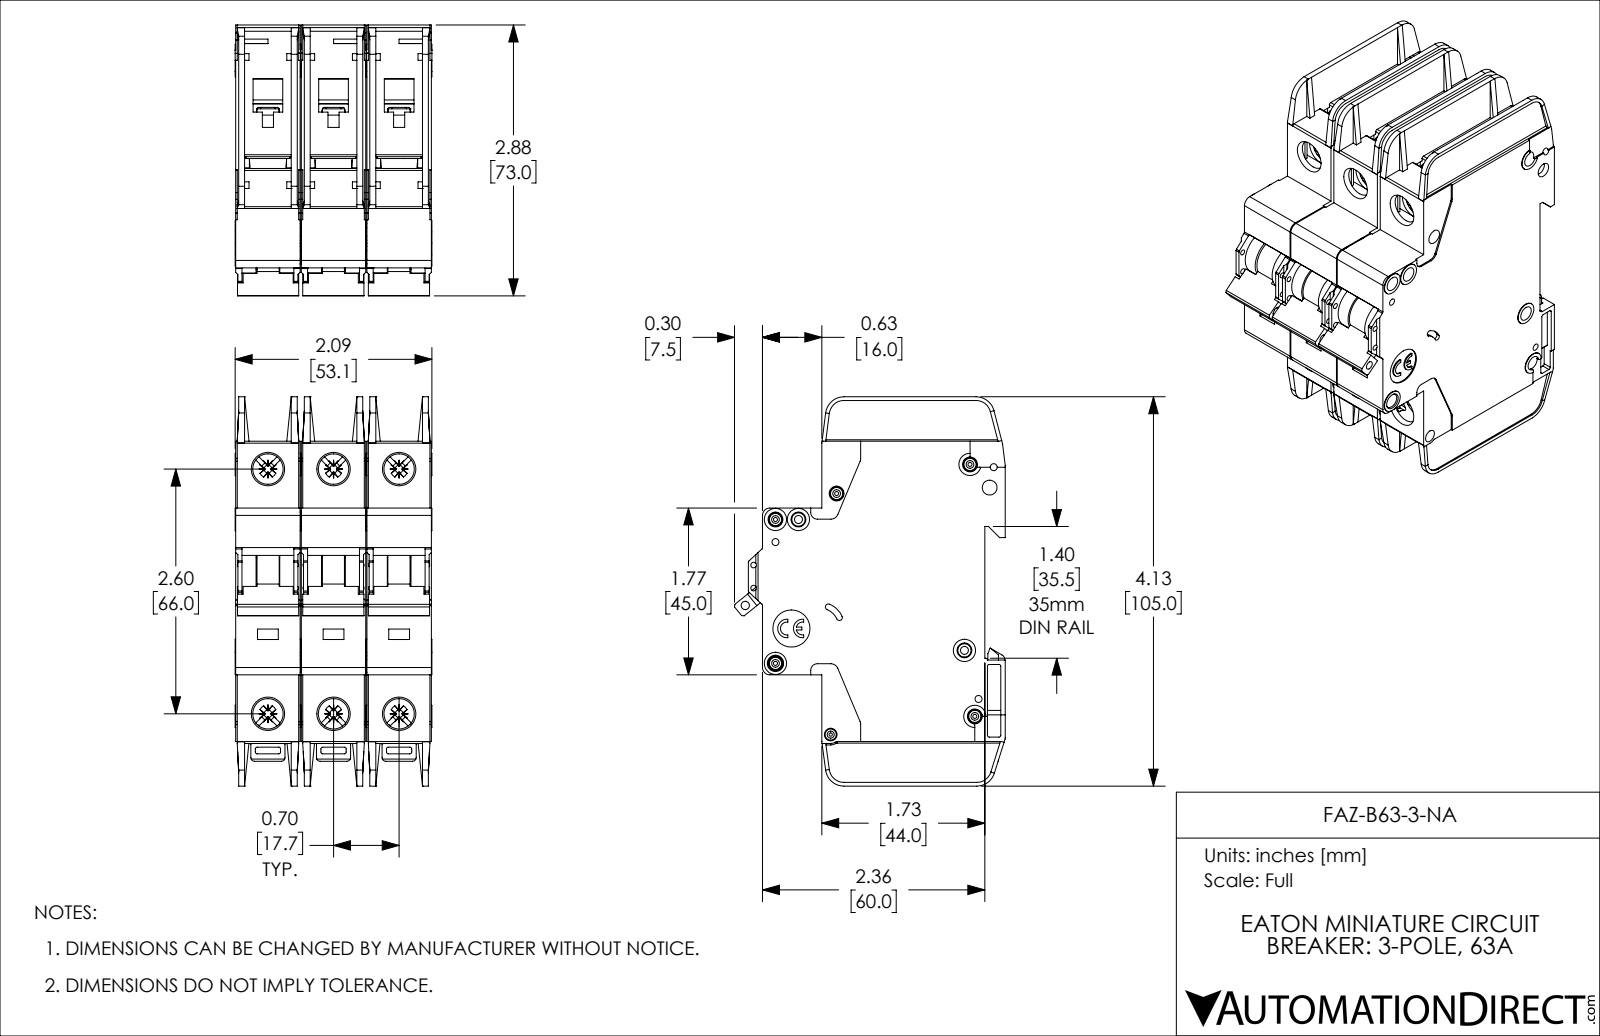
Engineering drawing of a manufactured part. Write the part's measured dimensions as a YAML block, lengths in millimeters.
part_name: "FAZ-B63-3-NA"
step_written_by: "SolidWorks 2019 (AUTOMOTIVE_DESIGN)"
units: millimeters
bodies: {solids: 3, faces: 3381, planar: 2013, cylindrical: 1071, other: 297}
overall_size: [105, 73.1, 53.1]
volume: 230200
surface_area: 79350
round_holes:
  - {diameter: 4, count: 8}
  - {diameter: 8.2, count: 6}
  - {diameter: 1.1, count: 5}
  - {diameter: 1.9, count: 4}
  - {diameter: 1.5, count: 2}
  - {diameter: 2.2, count: 2}
  - {diameter: 0.9, count: 1}
  - {diameter: 2.3, count: 1}
  - {diameter: 2.5, count: 1}
  - {diameter: 3.4, count: 1}
  - {diameter: 10, count: 1}
round_bosses_or_shafts:
  - {diameter: 3.3, count: 5}
  - {diameter: 6, count: 4}
  - {diameter: 3, count: 4}
  - {diameter: 2.5, count: 3}
partial_cylinders:
  - {radius: 0.5, count: 72}
  - {radius: 0.4, count: 30}
  - {radius: 1, count: 18}
  - {radius: 1.1, count: 12}
  - {radius: 2, count: 12}
  - {radius: 0.2, count: 6}
  - {radius: 0.3, count: 6}
  - {radius: 0.7, count: 6}
face_to_face_distances: [17.7, 1.2, 35.4, 17.4, 15, 35.1, 18.9, 16.5, 2.7, 2.4]
hole_center_spacings: [17.7, 68.3, 66, 6.2, 13.6, 22.1, 35.4, 74.9]
